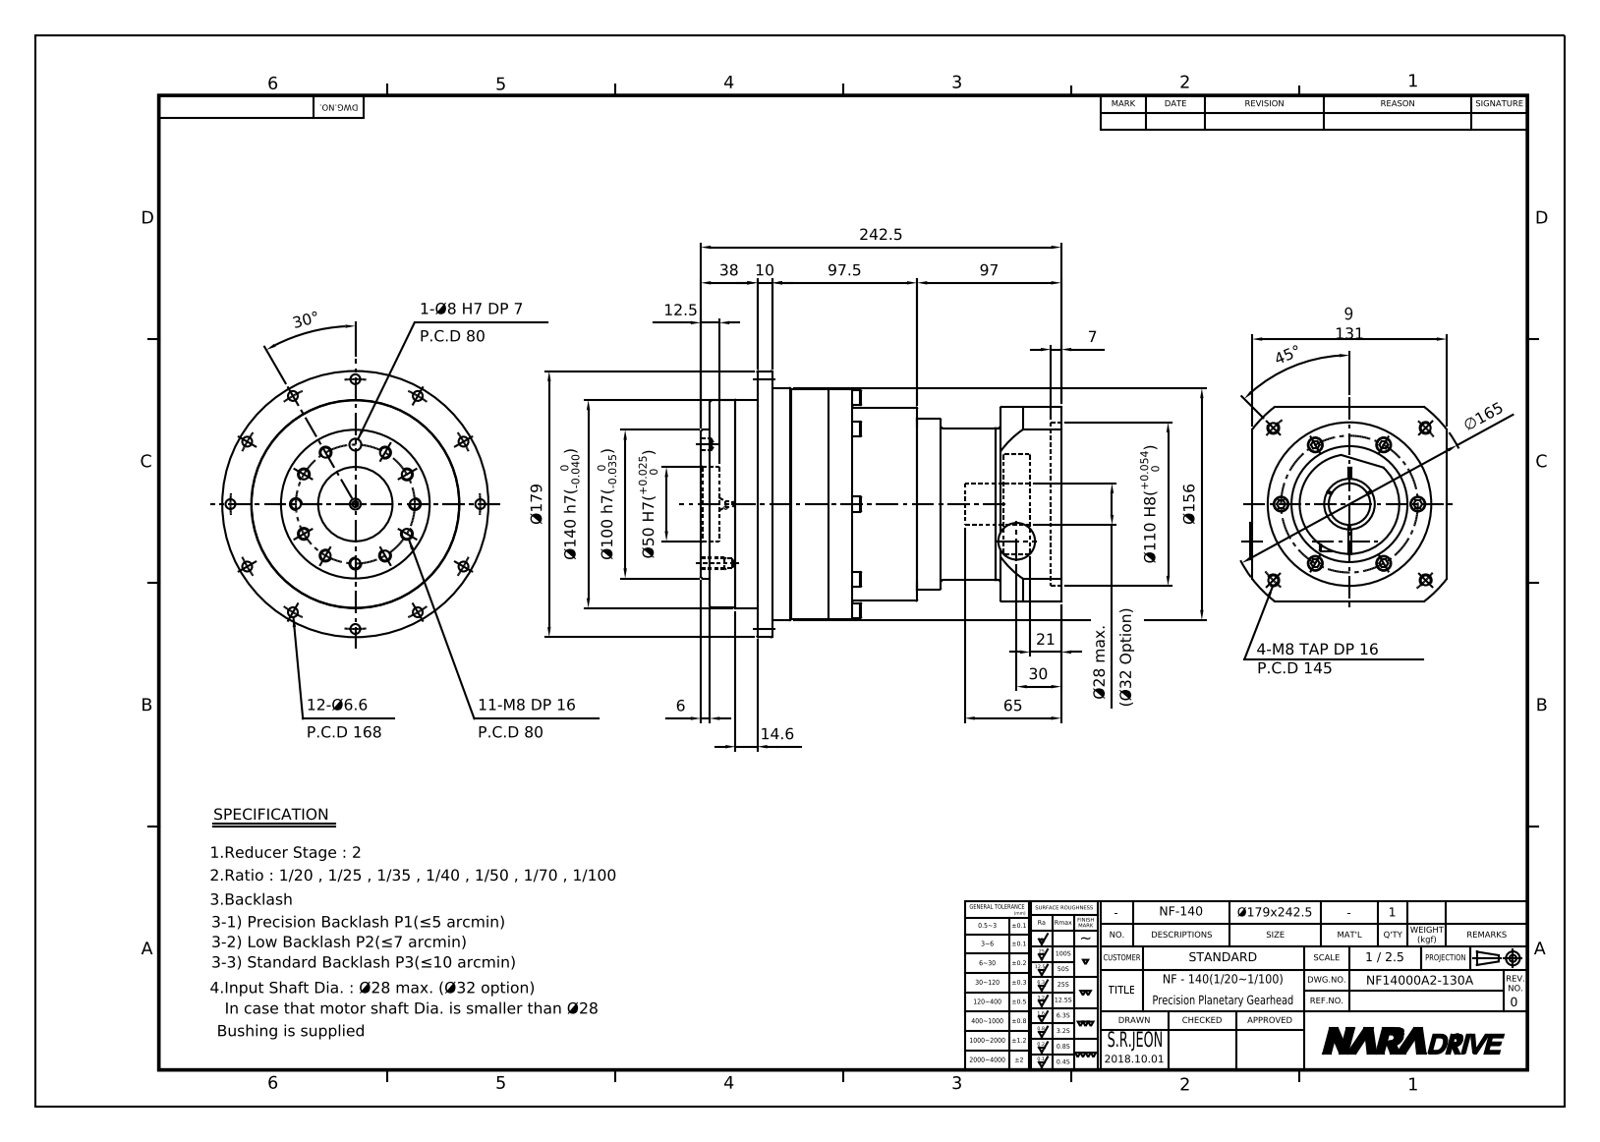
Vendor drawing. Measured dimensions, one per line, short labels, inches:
name: NF14000A2-130A
written by: Autodesk Inventor 2015 (AUTOMOTIVE_DESIGN)
unit: in
bodies: 2 solids, 598 faces (263 planar, 172 cylindrical, 163 other)
size: 9.547 × 7.047 × 7.047
volume: 152.6 in³; area: 499.2 in²
holes: 30× ⌀0.26, 18× ⌀0.194, 16× ⌀0.262, 10× ⌀0.433, 1× ⌀0.157, 1× ⌀0.315, 1× ⌀0.492, 1× ⌀0.571, 1× ⌀1.102, 1× ⌀1.339, 1× ⌀1.969, 1× ⌀2.835
bosses: 18× ⌀0.394, 18× ⌀0.236, 2× ⌀4.016, 1× ⌀7.047, 1× ⌀6.142, 1× ⌀6.102, 1× ⌀5.512, 1× ⌀5.472
rounds: 12× R0.039, 4× R0.02, 1× R0.177, 1× R0.276, 1× R2.559, 1× R3.248
face distances: 1.89, 0.197, 1.693, 0.748, 1.496, 2.295, 4.185, 2.343, 1.26, 1.654
hole spacings: 1.575, 2.097, 3.307, 3.663, 4.316, 1.732, 2.227, 2.728
